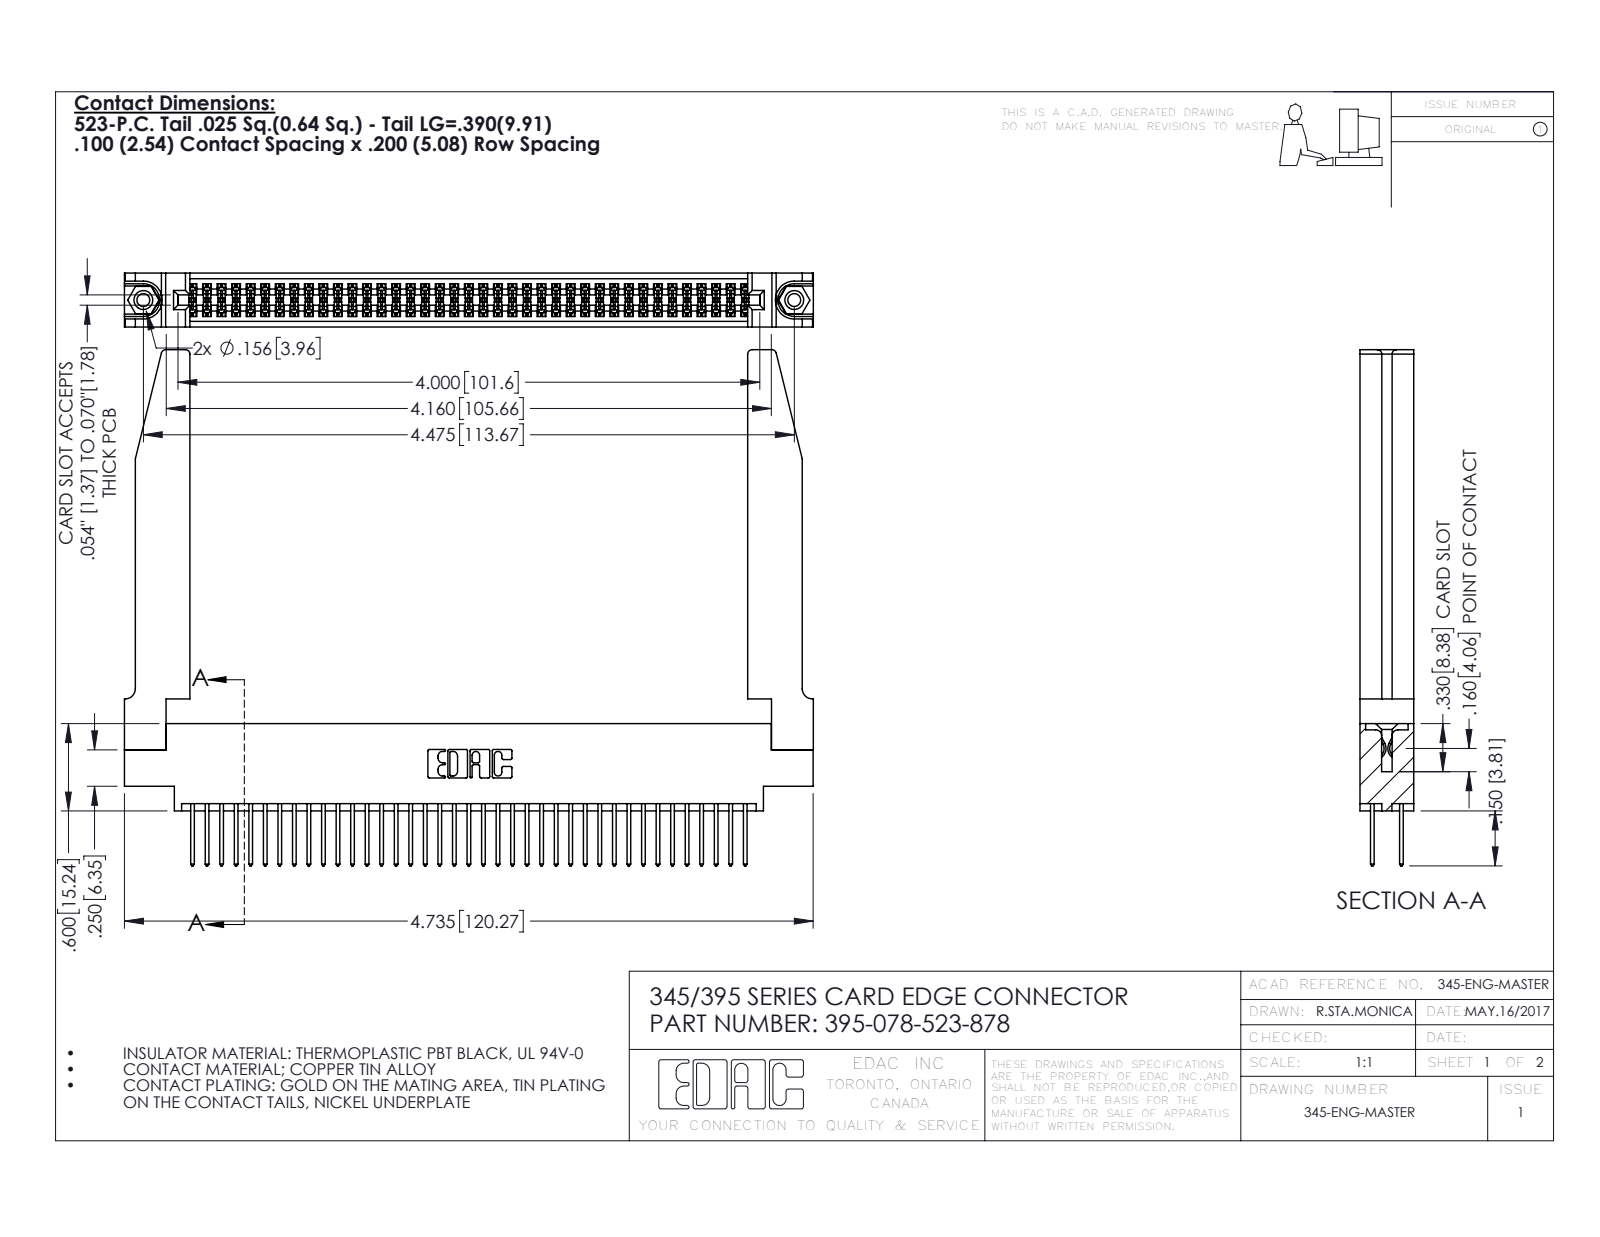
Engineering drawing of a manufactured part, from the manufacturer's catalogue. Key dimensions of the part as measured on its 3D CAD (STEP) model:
Part name (STEP PRODUCT): 345-220-078_345-220-078; 345-292-001_345-293-123; 345 Part_0.170 Offset - 0.156 Dia-TH; 395-078-523-878 (+1 more)
STEP written by: SolidWorks 2016 (CONFIG_CONTROL_DESIGN)
Units: inches
Bodies: 83 solids, 4264 faces (2800 planar, 1412 cylindrical, 52 other)
Overall size (bounding box): 4.736 × 3.547 × 0.37
Volume: 1.188 in³ · Surface area: 38.66 in²
Round holes (diameter × count): ⌀0.089 ×2, ⌀0.125 ×2, ⌀0.156 ×2, ⌀0.064 ×1
Round bosses / shafts (diameter × count): ⌀0.155 ×2
Partial cylindrical surfaces — rounded edges, fillets, slot ends (radius × count): R0.006 ×117, R0.01 ×78, R0.01 ×22, R0.03 ×8, R0.007 ×6, R0.031 ×6, R0.026 ×3, R0.014 ×2
Main face-to-face distances: 0.072, 0.37, 0.298, 0.2, 0.098, 0.272, 0.025, 0.225, 0.175, 0.148
Hole centre spacings: 0.27, 4.239, 4.475
